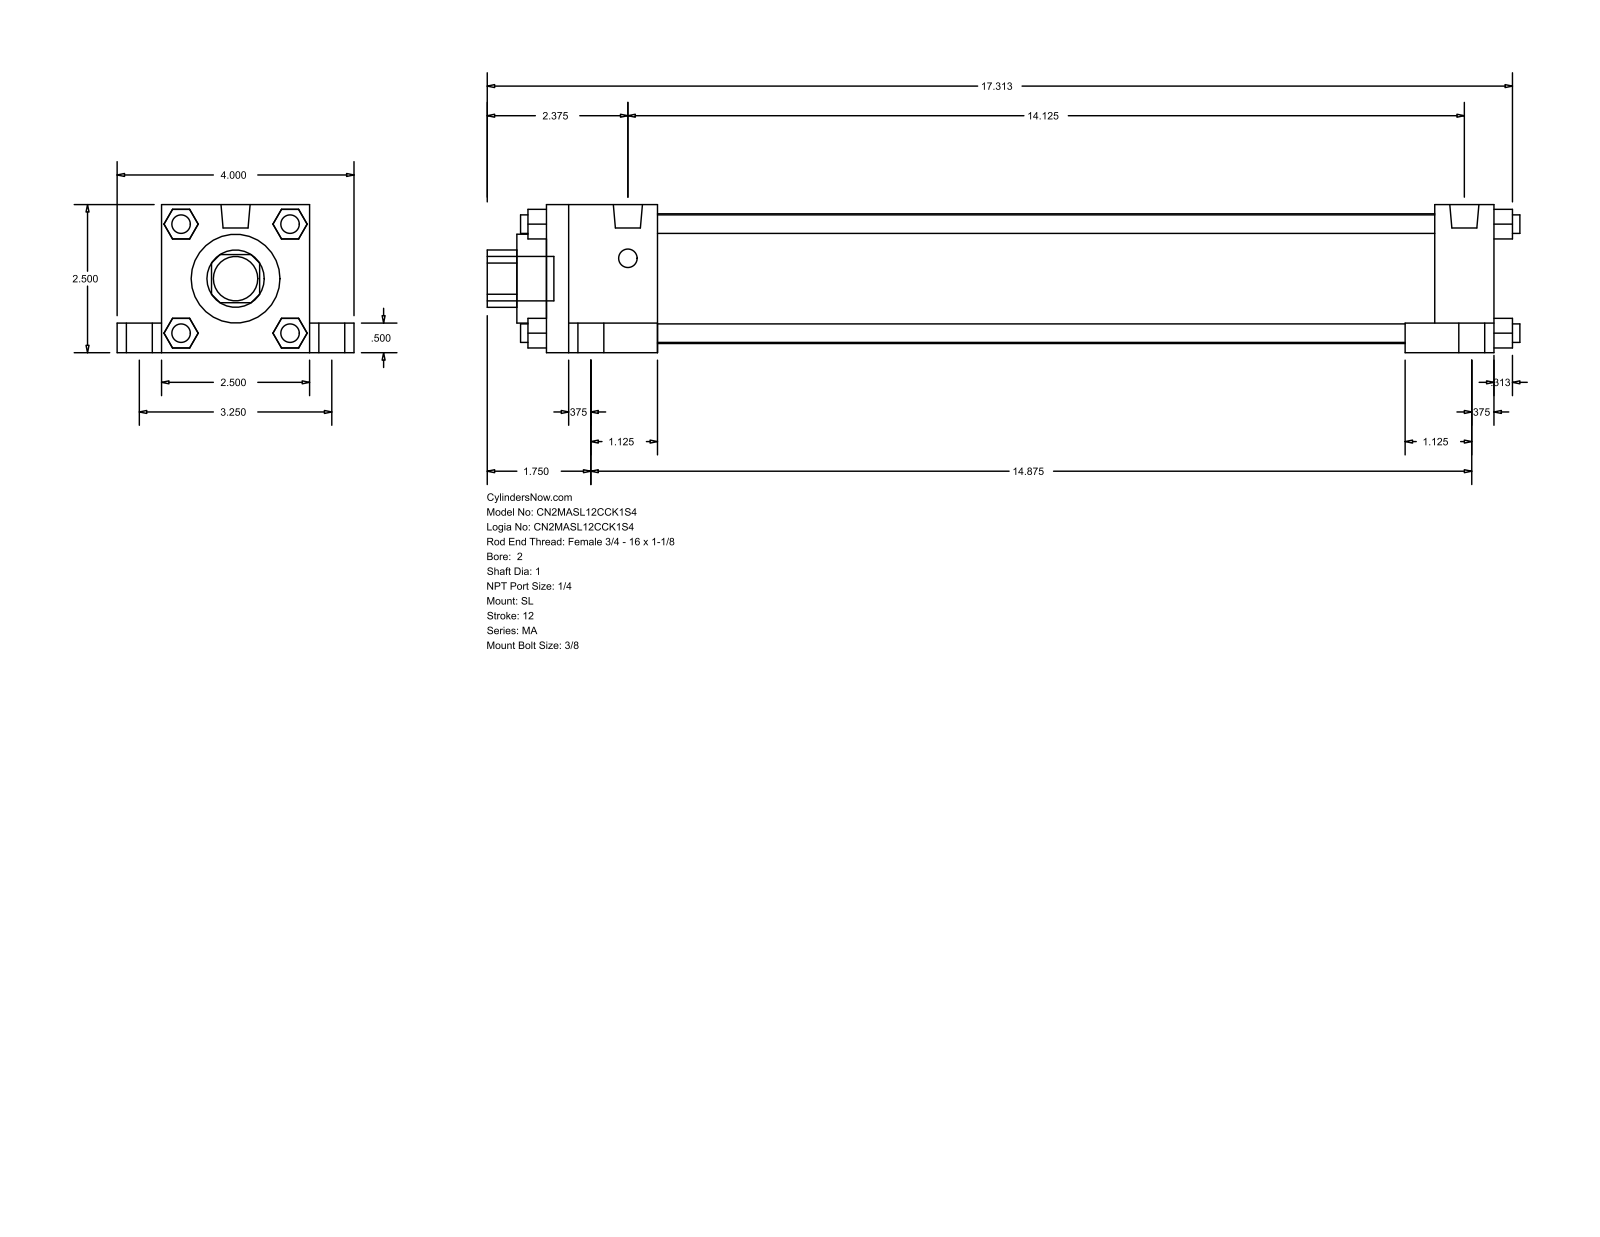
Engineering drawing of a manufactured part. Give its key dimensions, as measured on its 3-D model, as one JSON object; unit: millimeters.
{"part_name": "MA_SL__0200_1", "step_written_by": "GSSL Pune (CONFIG_CONTROL_DESIGN)", "units": "millimeters", "bodies": {"solids": 0, "faces": 148, "planar": 112, "cylindrical": 36, "other": 0}, "overall_size": [442.91, 101.6, 63.5], "round_holes": [[25.4, 1], [38.1, 1], [55.63, 1]], "round_bosses_or_shafts": [[7.94, 8], [17.46, 4], [11.11, 4], [12.49, 2], [19.05, 1]], "partial_cylinders_radius": [[12.29, 1]], "face_to_face_distances": [63.5, 12.7, 406.4, 19.05, 82.55, 25.4, 50.8, 47.63, 358.77, 381]}
